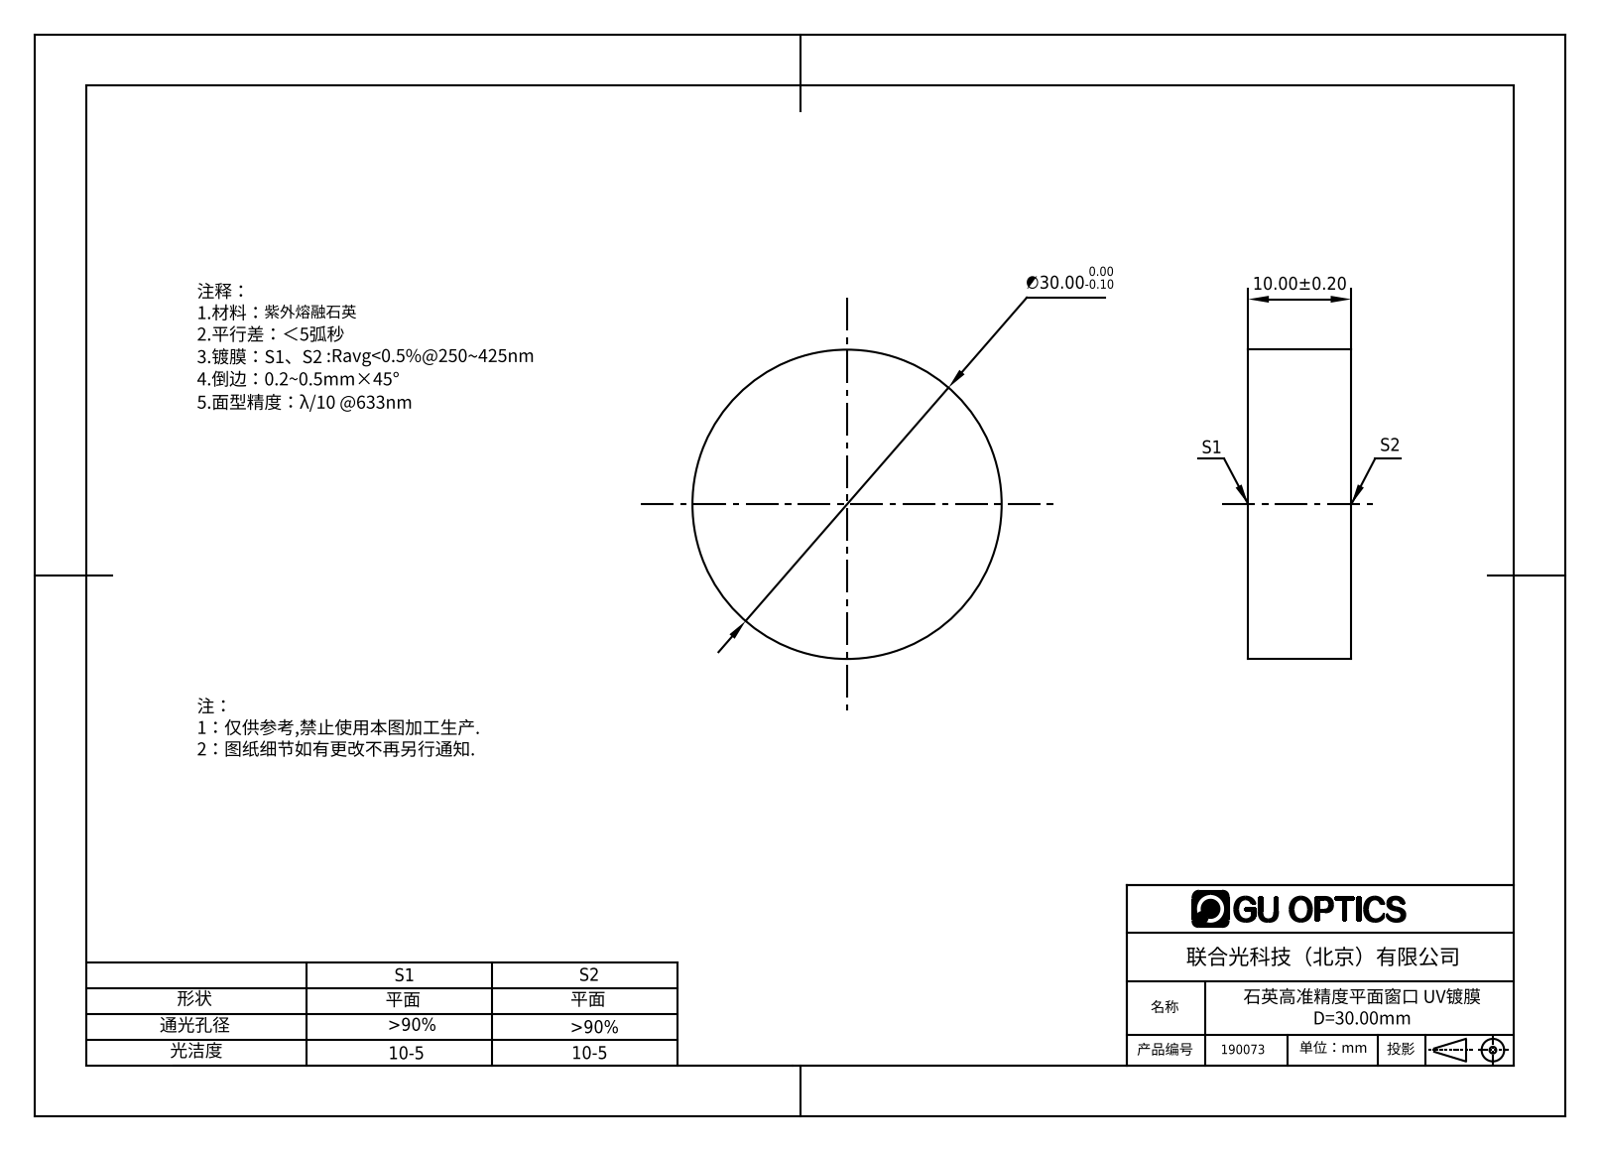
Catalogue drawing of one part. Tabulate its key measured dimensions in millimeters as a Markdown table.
| quantity | value |
| --- | --- |
| part name | 190062 |
| STEP written by | SolidWorks 2016 (AUTOMOTIVE_DESIGN) |
| units | millimeters |
| bodies | 1 solid, 4 faces (2 planar, 2 cylindrical, 0 other) |
| overall size | 30 × 30 × 10 |
| volume | 7 069 mm³ |
| surface area | 2 356 mm² |
| round bosses / shafts (diameter × count) | 30 × 1 |
| main face-to-face distances | 10 |
